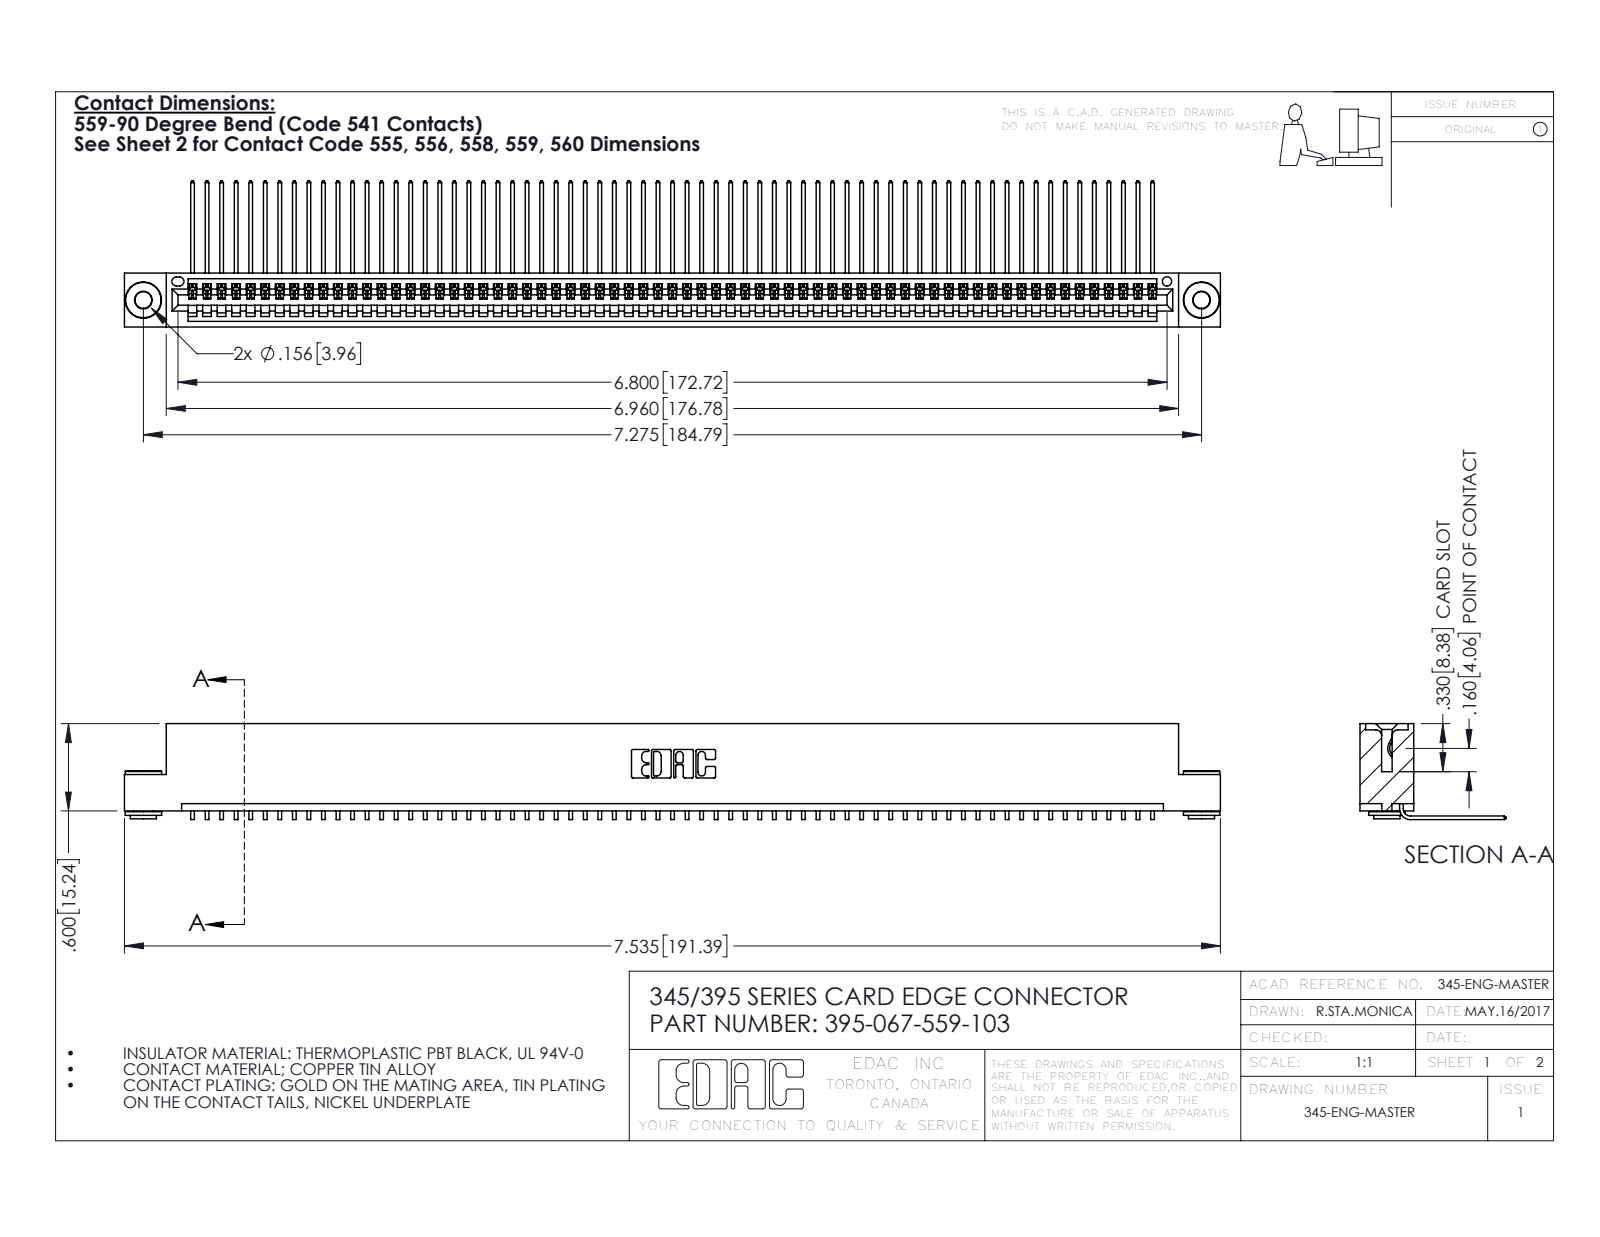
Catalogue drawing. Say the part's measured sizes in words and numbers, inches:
The part is named "345-292-001_558 559 Tail - 1; 395-067-559-103; 345-250-002_345-250-002-102; 345 Part_Flush Mounting Lugs - 0.156 Dia-TH". Its 3-D file was written by "SolidWorks 2016 (CONFIG_CONTROL_DESIGN)". It is 70 solids with 4184 faces: 2904 planar, 1272 cylindrical and 8 other. Overall it measures 7.535 by 1.005 by 0.659 inches. Its volume is 1.137 cubic inches and its surface area 41.26 square inches. Round holes: 2 of diameter 0.116, 2 of diameter 0.156, 1 of diameter 0.064. Round bosses or shafts: 2 of diameter 0.25, 2 of diameter 0.18, 2 of diameter 0.136. Partial cylindrical surfaces (rounded edges, fillets, slot ends): 134 of radius 0.006, 22 of radius 0.01, 6 of radius 0.007, 6 of radius 0.031, 3 of radius 0.026, 2 of radius 0.031, 2 of radius 0.04, 1 of radius 0.014. The main face-to-face distances are 0.072, 0.298, 0.37, 0.2, 0.025, 0.098, 0.272, 0.225, 0.149, 0.072. The hole center spacings are 0.27, 7.039, 7.275.
